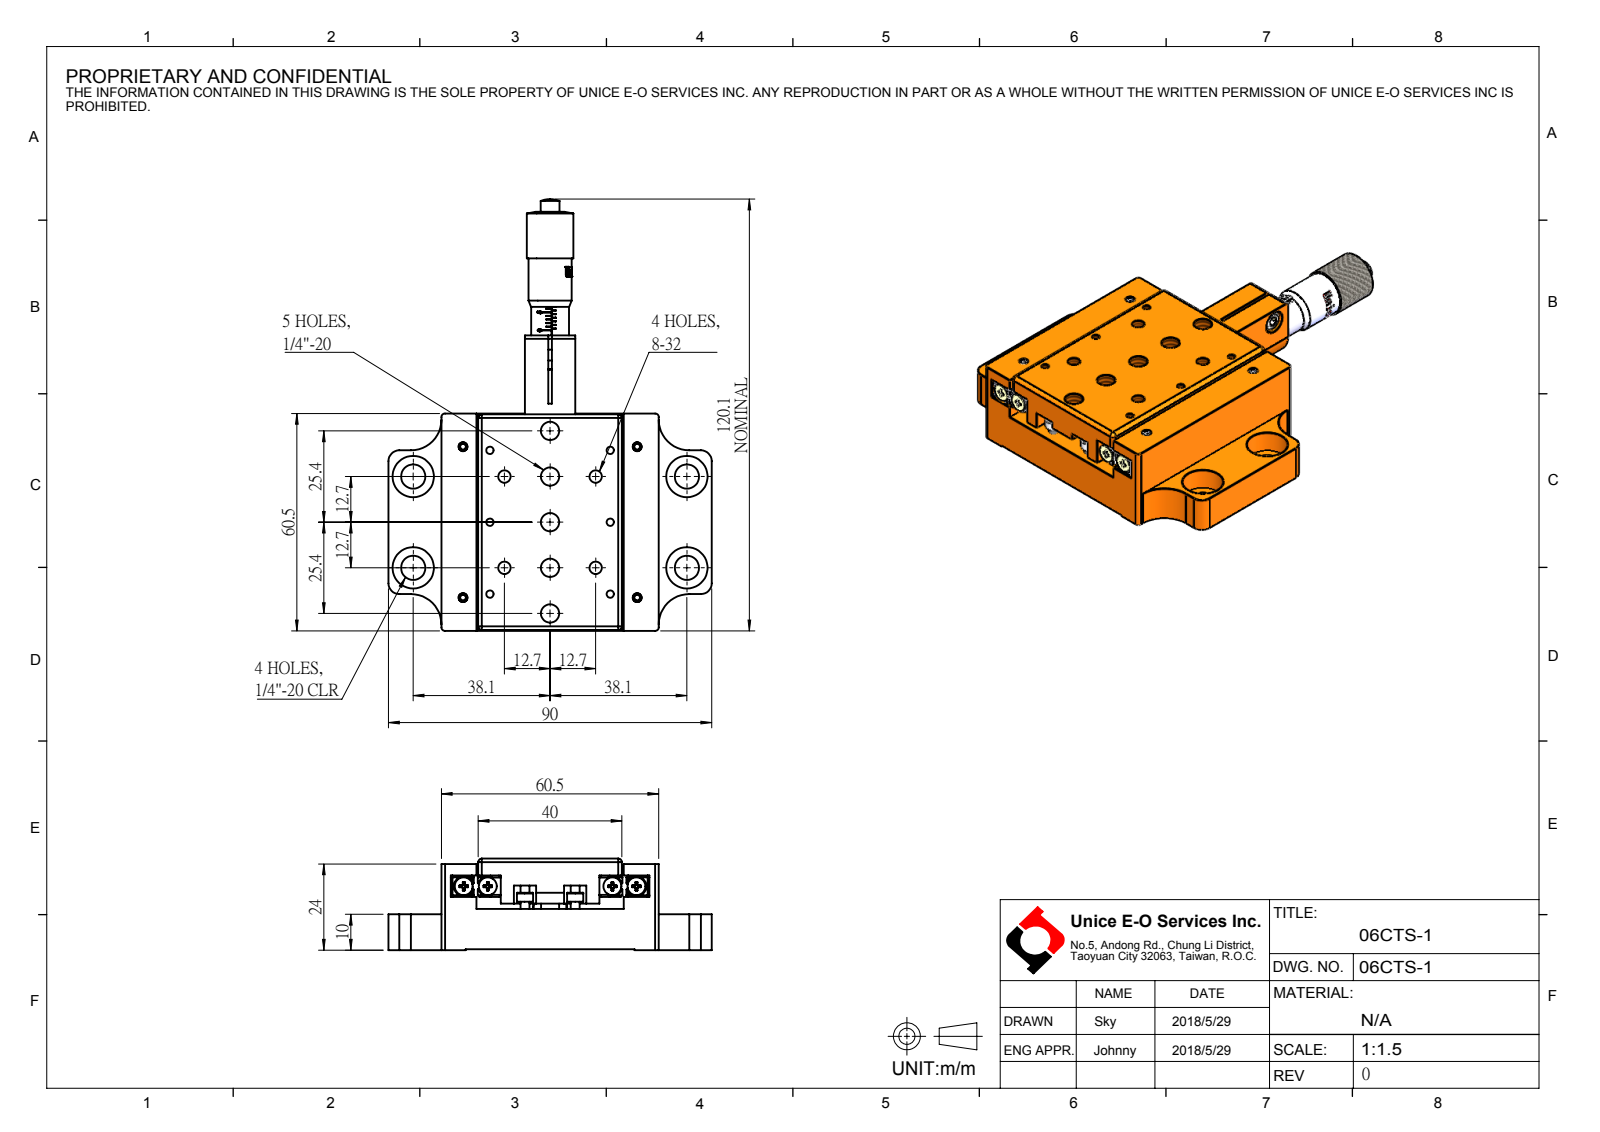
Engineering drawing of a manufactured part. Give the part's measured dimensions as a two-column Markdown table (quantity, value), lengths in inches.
| quantity | value |
| --- | --- |
| part name | 06CTS-1 |
| STEP written by | SolidWorks 2016 (AUTOMOTIVE_DESIGN) |
| units | inches |
| bodies | 0 solids, 610 faces (362 planar, 147 cylindrical, 101 other) |
| overall size | 4.73 × 3.543 × 1.004 |
| round holes (diameter × count) | 0.098 × 8, 0.081 × 6, 0.201 × 5, 0.136 × 4, 0.266 × 4, 0.453 × 4, 0.256 × 1, 0.315 × 1, 0.374 × 1, 0.417 × 1 |
| round bosses / shafts (diameter × count) | 0.197 × 5, 0.177 × 2, 0.098 × 2, 0.512 × 1, 0.472 × 1, 0.413 × 1, 0.362 × 1, 0.205 × 1 |
| partial cylindrical surfaces (radius × count) | 0.039 × 13, 0.118 × 4, 0.335 × 4, 0.235 × 1, 0.276 × 1 |
| main face-to-face distances | 0.551, 0.059, 0.236, 0.441, 0.453, 0.992, 1.004, 0.126, 0.492, 2.382 |
| hole center spacings | 1, 1.581, 0.5, 0.707, 1.414, 1.5, 2, 0.298 |
